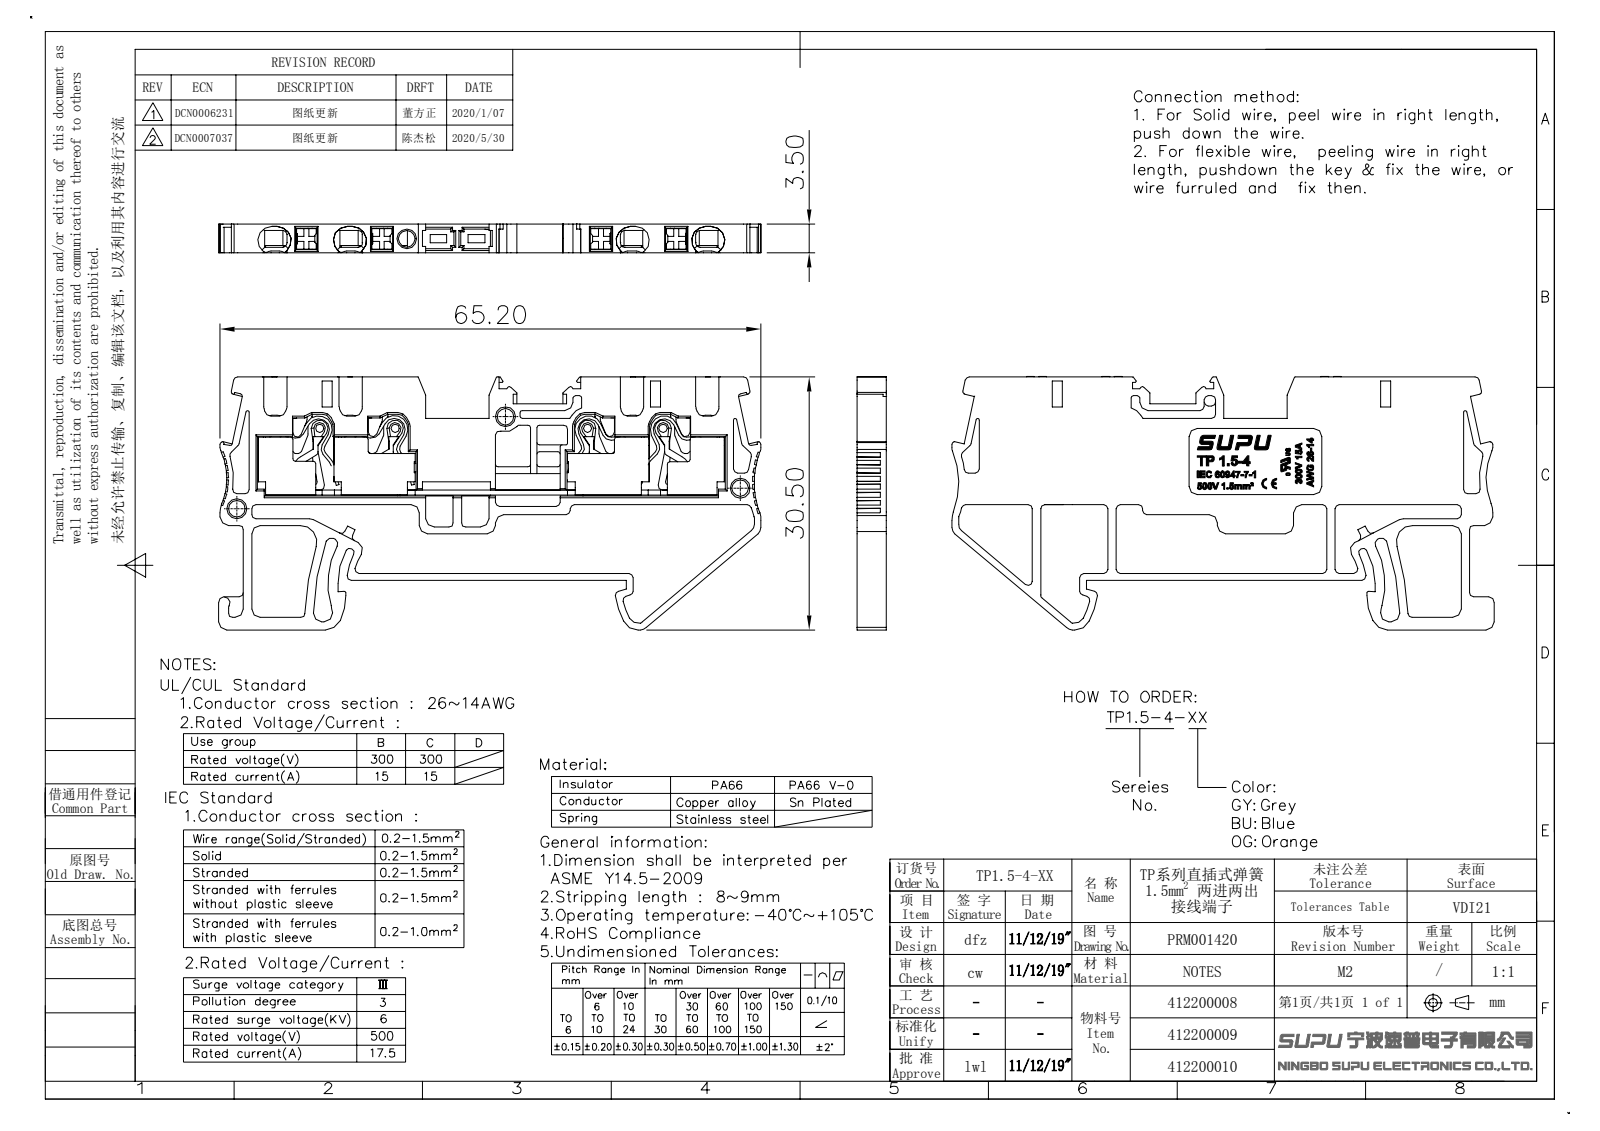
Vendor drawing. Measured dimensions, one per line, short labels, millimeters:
name: TP1.5-4-GY_stp
written by: SIEMENS PLM Software NX 10.0 (CONFIG_CONTROL_DESIGN)
unit: mm
bodies: 1 solid, 1855 faces (1646 planar, 117 cylindrical, 92 other)
size: 65.4 × 30.5 × 3.5
volume: 4 928 mm³; area: 4 396 mm²
holes: 1× ⌀0.7, 1× ⌀2
rounds: 11× R1, 10× R0.1, 10× R0.3, 10× R0.5, 8× R1.7, 4× R0.15, 4× R1.28, 3× R0.2
face distances: 3.5, 3.45, 0.5, 24.5, 2.3, 3, 22.2, 0.4, 2.5, 1
